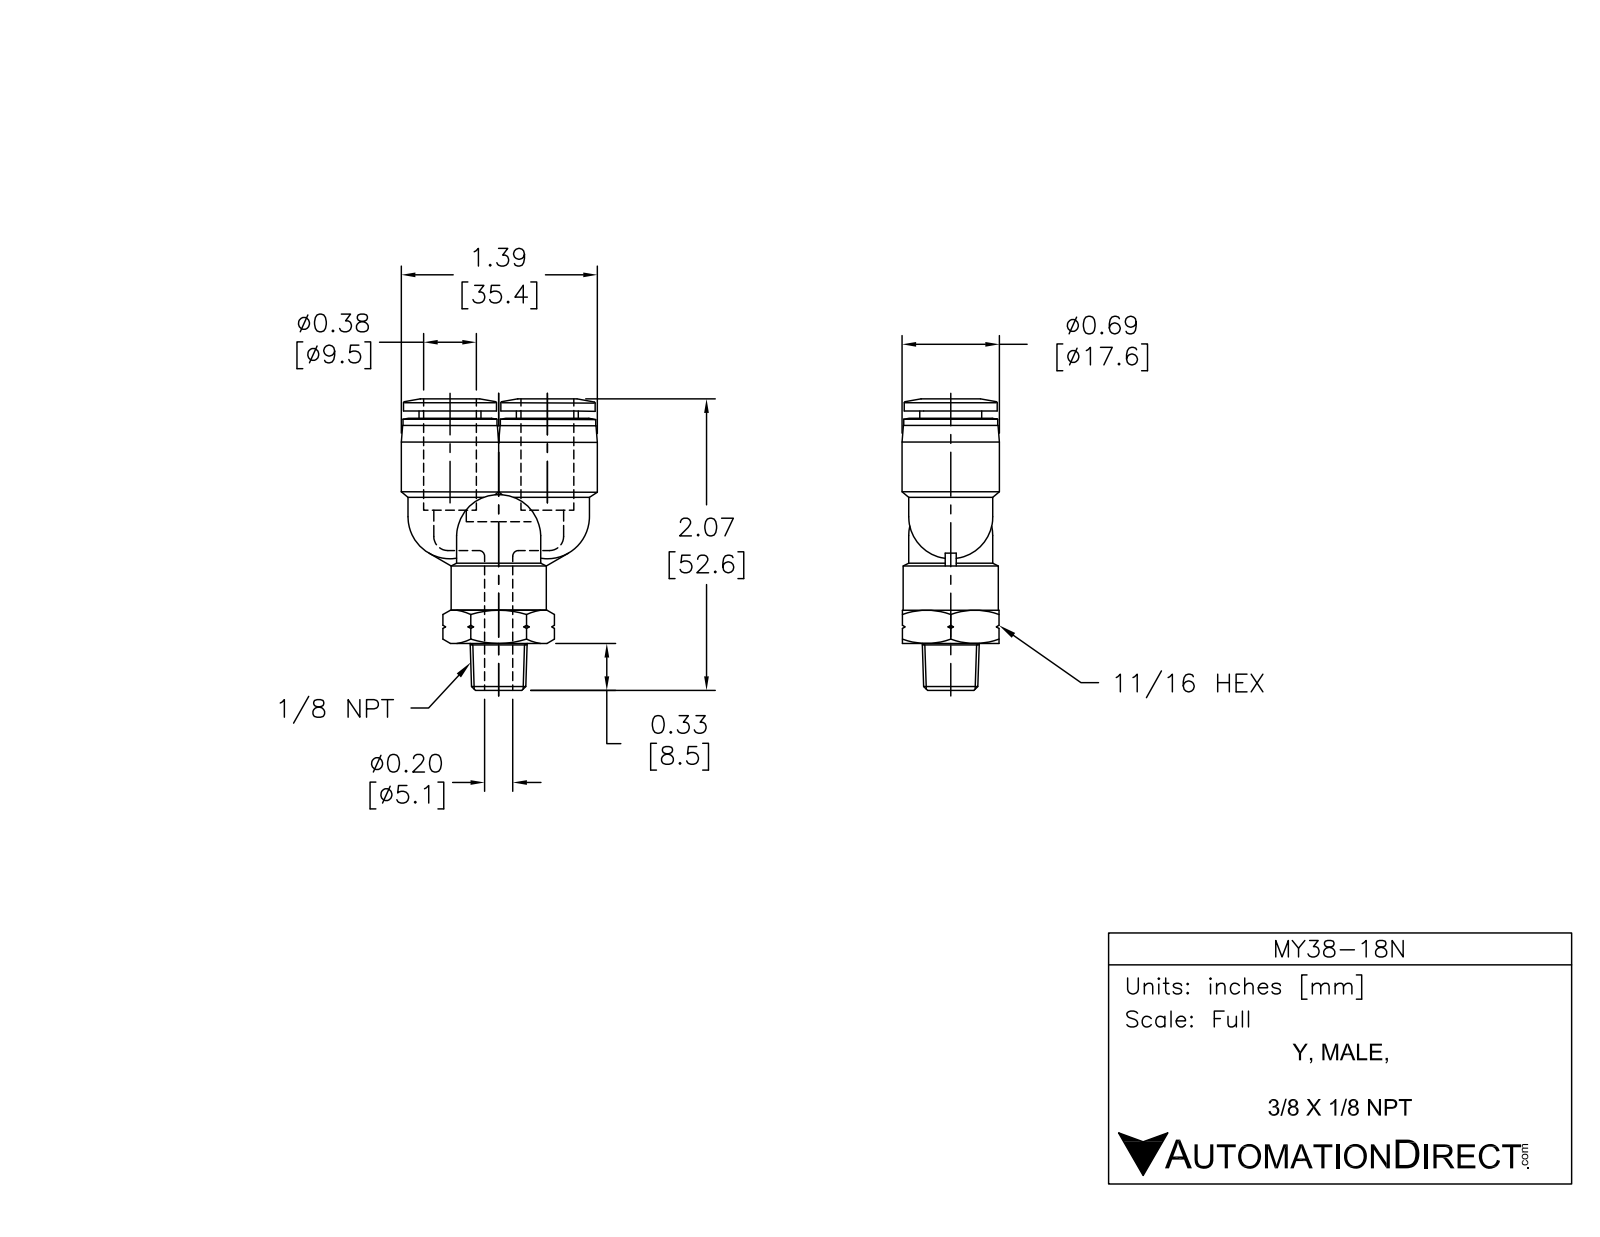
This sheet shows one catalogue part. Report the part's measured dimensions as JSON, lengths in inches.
{"part_name": "MY38-18N", "step_written_by": "SolidWorks 2015 (AUTOMOTIVE_DESIGN)", "units": "inches", "bodies": {"solids": 1, "faces": 125, "planar": 22, "cylindrical": 32, "other": 71}, "overall_size": [2.075, 1.386, 0.693], "volume_in3": 0.765, "surface_area_in2": 10.93, "round_holes": [[0.386, 2], [0.197, 1]], "round_bosses_or_shafts": [[0.598, 3], [0.693, 2], [0.669, 2], [0.661, 2], [0.441, 2], [0.677, 1]], "face_to_face_distances": [0.687, 0.051, 1.602, 1.654, 0.709, 0.945, 0.657, 0.335, 1.28, 1.937], "hole_center_spacings": [0.346, 0.693]}
